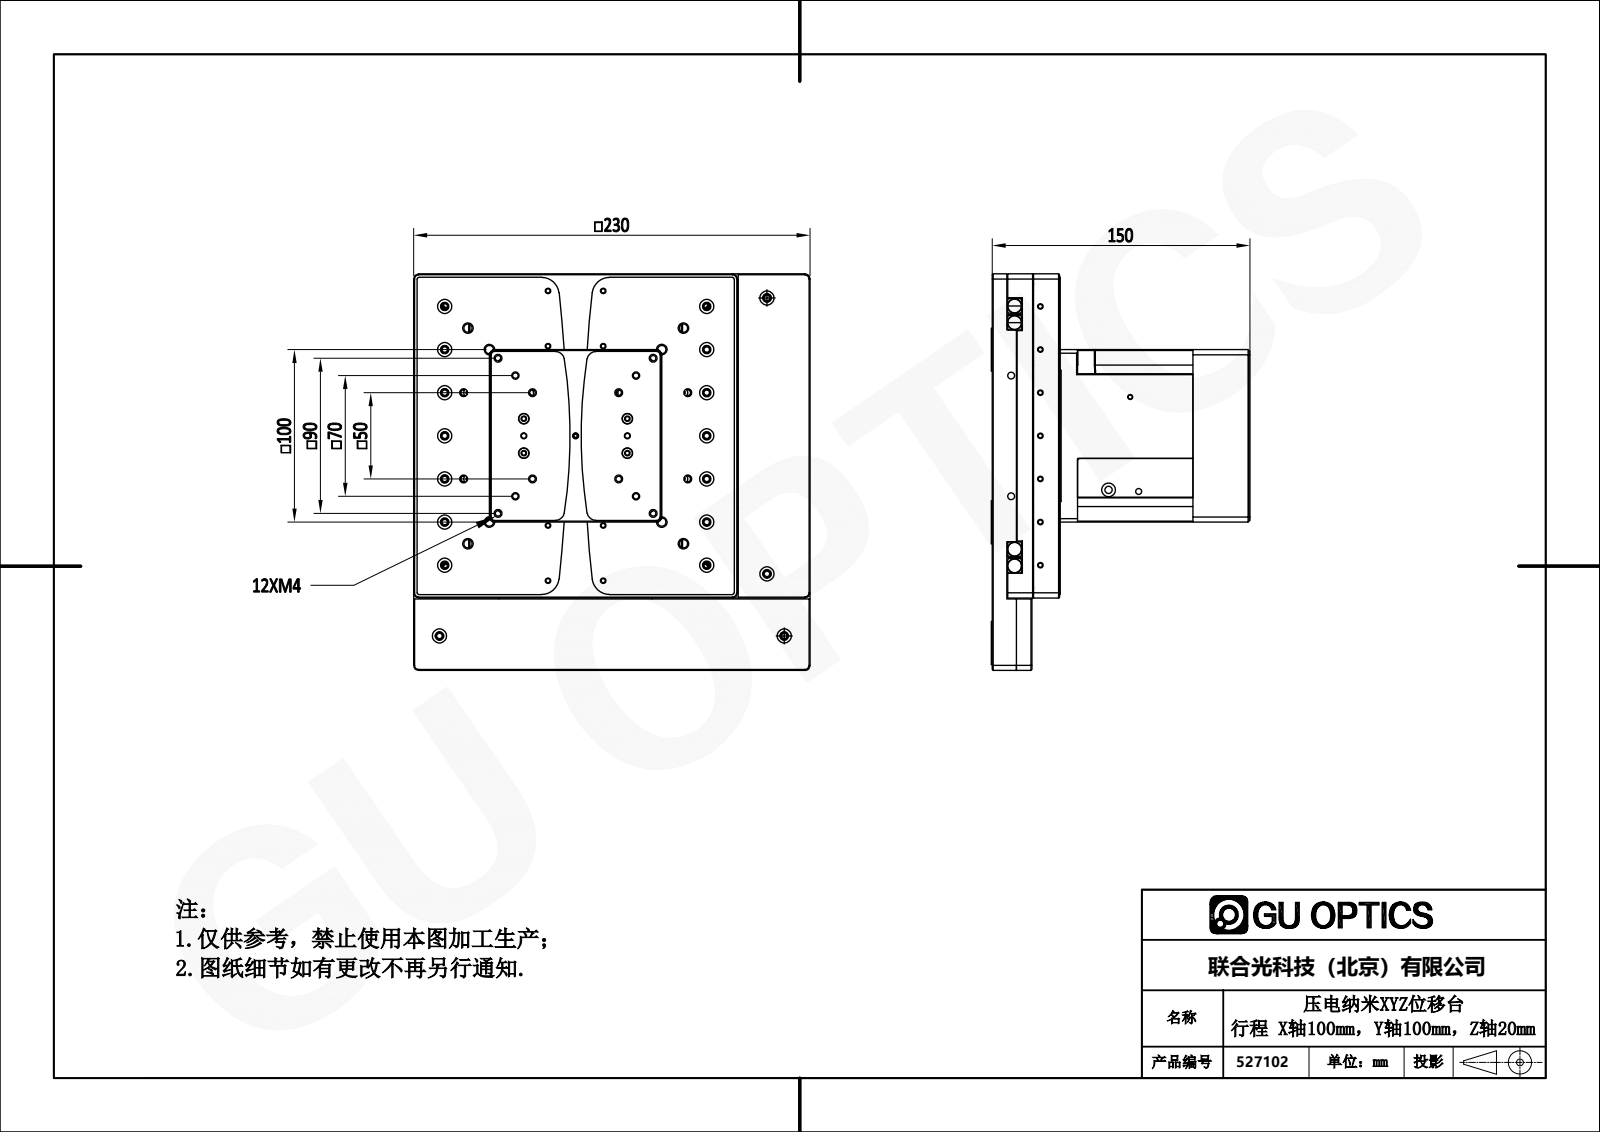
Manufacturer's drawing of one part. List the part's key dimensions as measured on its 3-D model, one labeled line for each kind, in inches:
Part name (STEP PRODUCT): 527102
STEP written by: SolidWorks 2020 (CONFIG_CONTROL_DESIGN)
Units: inches
Bodies: 32 solids, 4099 faces (2372 planar, 998 cylindrical, 729 other)
Overall size (bounding box): 9.055 × 9.055 × 5.906
Volume: 149.4 in³ · Surface area: 1 027 in²
Round holes (diameter × count): ⌀0.13 ×81, ⌀0.098 ×71, ⌀0.169 ×67, ⌀0.325 ×65, ⌀0.236 ×63, ⌀0.126 ×18, ⌀0.177 ×12, ⌀0.197 ×12, ⌀0.276 ×12, ⌀0.256 ×10, ⌀0.315 ×10, ⌀0.081 ×8
Round bosses / shafts (diameter × count): ⌀0.118 ×100, ⌀0.157 ×7, ⌀0.374 ×4, ⌀0.205 ×4
Partial cylindrical surfaces — rounded edges, fillets, slot ends (radius × count): R0.118 ×165, R0.197 ×34, R0.157 ×31, R0.098 ×20, R0.122 ×13, R0.02 ×12, R0.039 ×8, R0.059 ×8
Main face-to-face distances: 0.02, 0.61, 0.374, 0.591, 0.354, 0.571, 0.394, 0.63, 1.004, 0.236
Hole centre spacings: 0.984, 1.969, 2.953, 3.937, 5.212, 5.483, 4.921, 5.909
